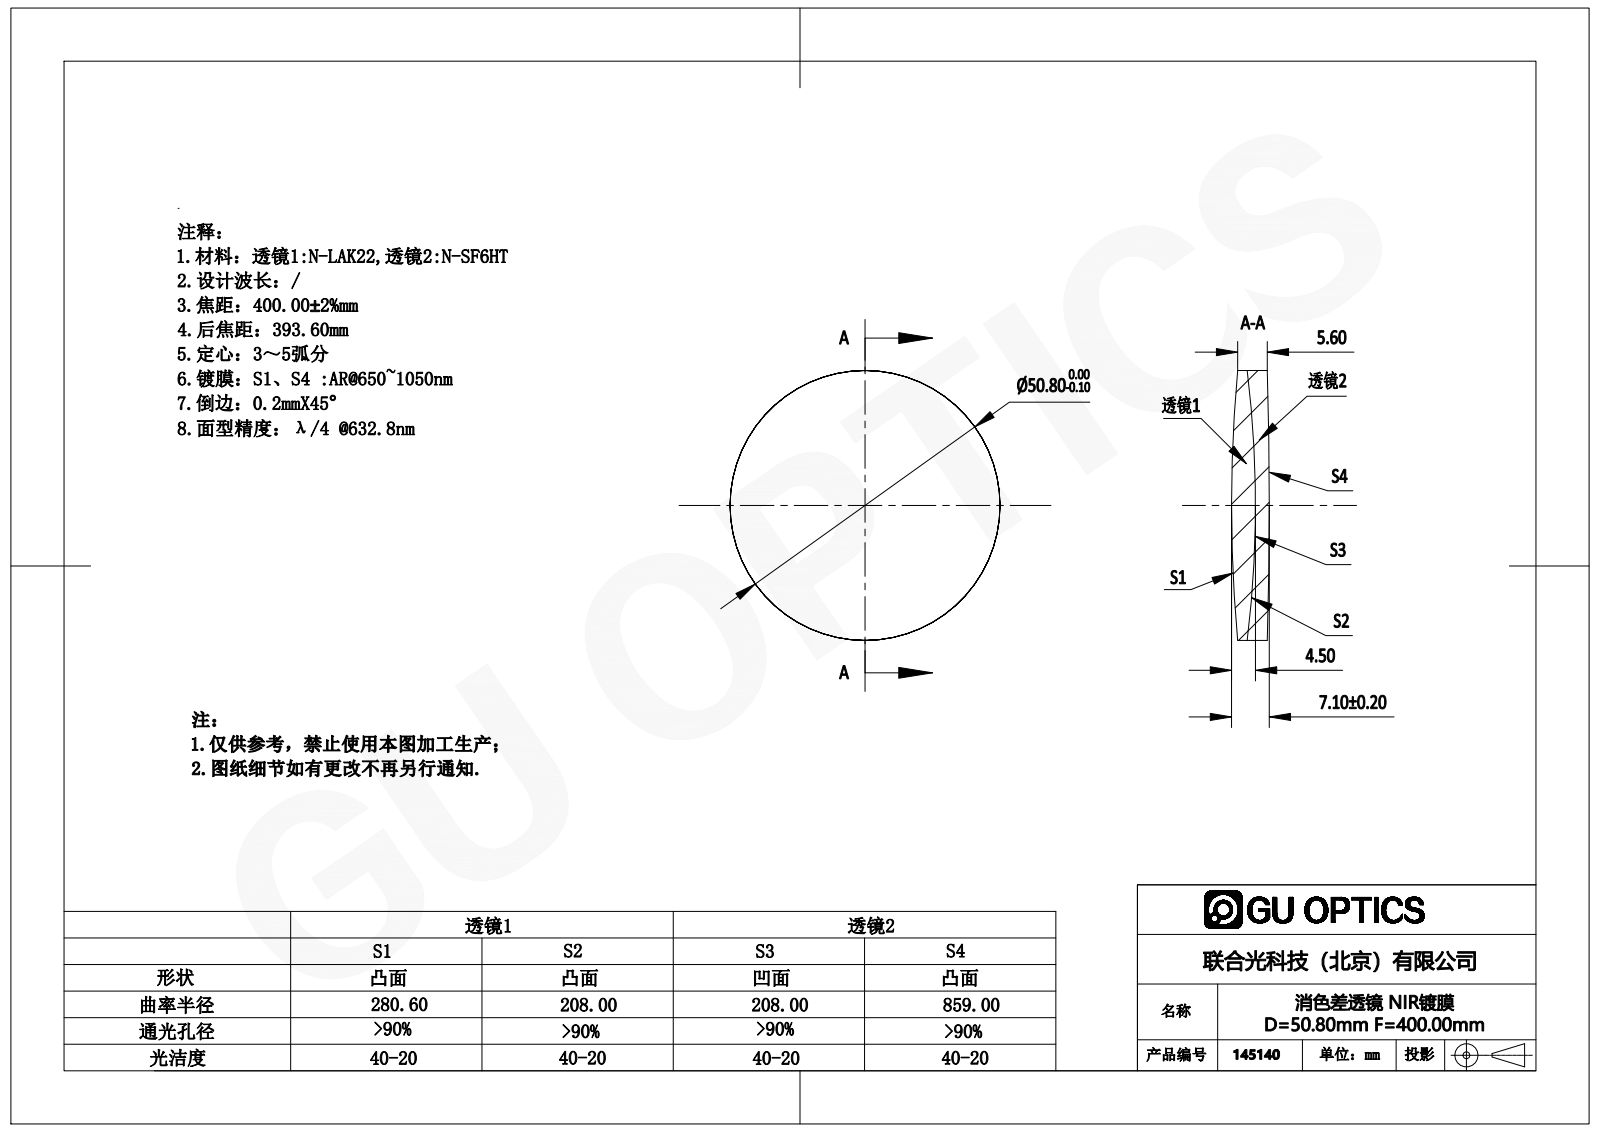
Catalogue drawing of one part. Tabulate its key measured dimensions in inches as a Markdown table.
| quantity | value |
| --- | --- |
| part name | 145140 |
| STEP written by | SolidWorks 2016 (AUTOMOTIVE_DESIGN) |
| units | inches |
| bodies | 2 solids, 12 faces (0 planar, 4 cylindrical, 8 other) |
| overall size | 2 × 2 × 0.28 |
| volume | 0.784 in³ |
| surface area | 13.97 in² |
| round bosses / shafts (diameter × count) | 2 × 1 |
